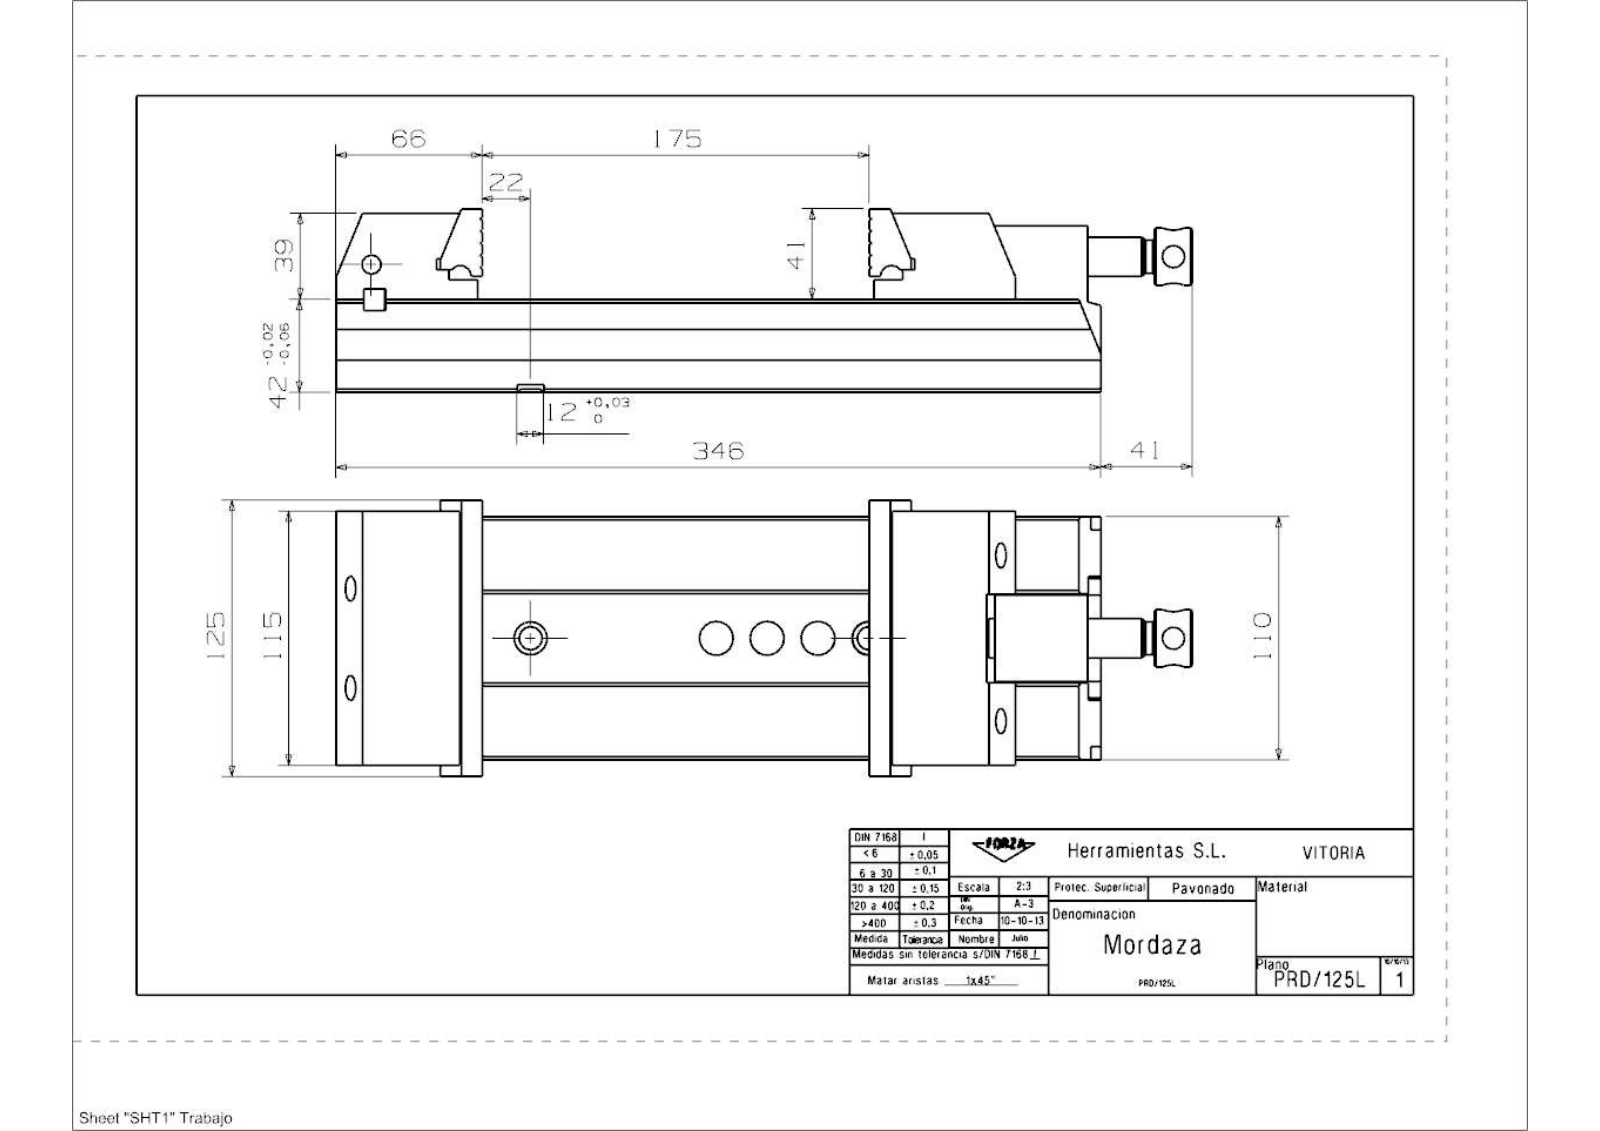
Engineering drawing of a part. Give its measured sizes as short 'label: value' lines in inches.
name: 30_125L_Mordaza
written by: SIEMENS PLM Software NX 7.5 (AUTOMOTIVE_DESIGN)
unit: in
bodies: 12 solids, 515 faces (320 planar, 147 cylindrical, 48 other)
size: 15.76 × 4.921 × 3.268
volume: 107.7 in³; area: 474.6 in²
holes: 4× ⌀0.171, 4× ⌀0.204, 4× ⌀0.256, 4× ⌀0.295, 4× ⌀0.453, 4× ⌀0.591, 3× ⌀0.346, 2× ⌀0.275, 2× ⌀0.315, 2× ⌀0.394, 2× ⌀0.413, 2× ⌀0.433
bosses: 1× ⌀1.024, 1× ⌀0.698, 1× ⌀0.591, 1× ⌀0.571, 1× ⌀0.413
rounds: 20× R0.012, 7× R0.236, 4× R0.394, 4× R0.63, 2× R0.063, 2× R0.197, 1× R0.118, 1× R0.315
face distances: 1.654, 0.606, 1.047, 0.335, 1.063, 3.031, 1.161, 1.535, 3.268, 0.531
hole spacings: 2.362, 0.362, 0.591, 0.923, 0.935, 0.988, 1.499, 1.732
